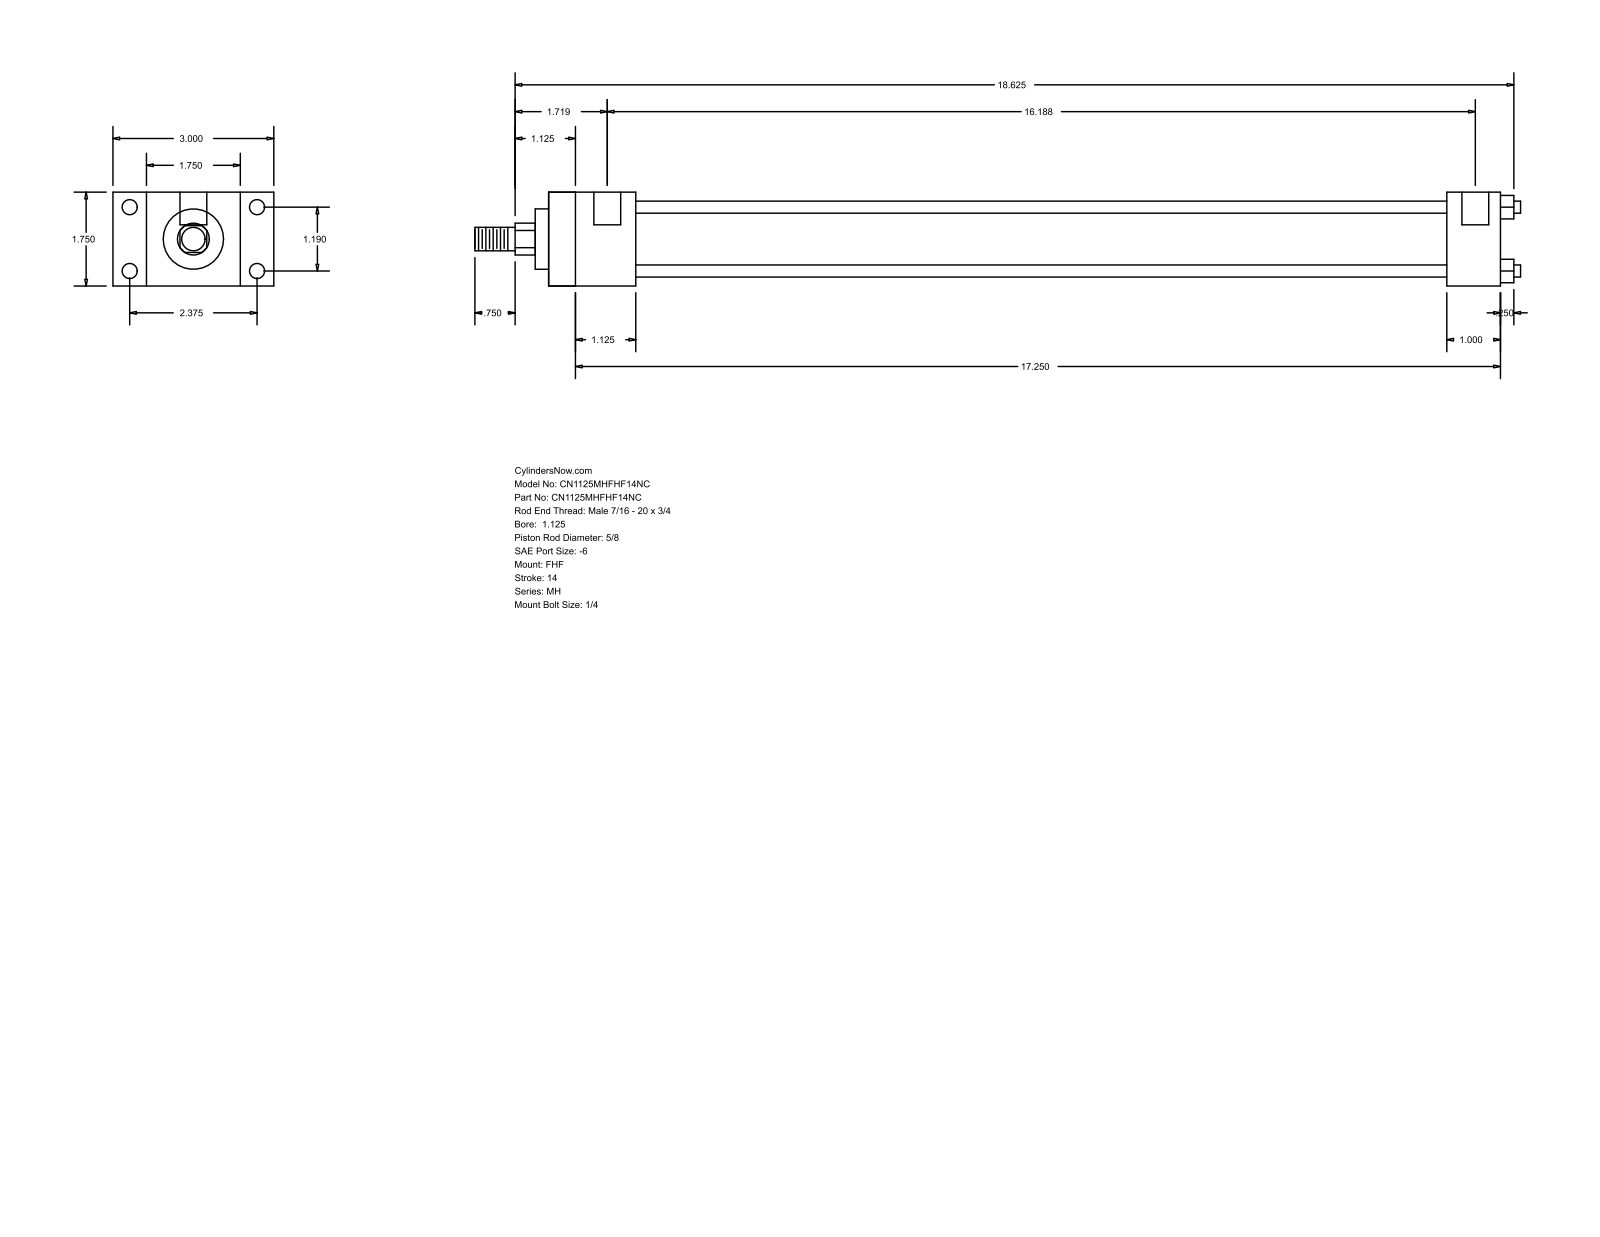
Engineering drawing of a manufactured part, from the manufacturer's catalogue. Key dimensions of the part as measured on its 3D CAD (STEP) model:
Part name (STEP PRODUCT): MH_FHF__0112_0.625
STEP written by: GSSL Pune (CONFIG_CONTROL_DESIGN)
Units: millimetres
Bodies: 0 solids, 88 faces (60 planar, 28 cylindrical, 0 other)
Overall size (bounding box): 495.3 × 76.2 × 44.45
Round holes (diameter × count): ⌀5.56 ×4, ⌀7.14 ×4, ⌀12.7 ×2
Round bosses / shafts (diameter × count): ⌀5.71 ×4, ⌀34.92 ×1, ⌀28.57 ×1, ⌀15.88 ×1, ⌀11.11 ×1
Partial cylindrical surfaces — rounded edges, fillets, slot ends (radius × count): R7.54 ×1
Main face-to-face distances: 44.46, 15.87, 60.33, 41.27, 76.2, 450.85, 409.58, 425.44, 384.17, 25.41
Hole centre spacings: 30.22, 60.32, 67.47, 407.99, 3.17, 411.16
